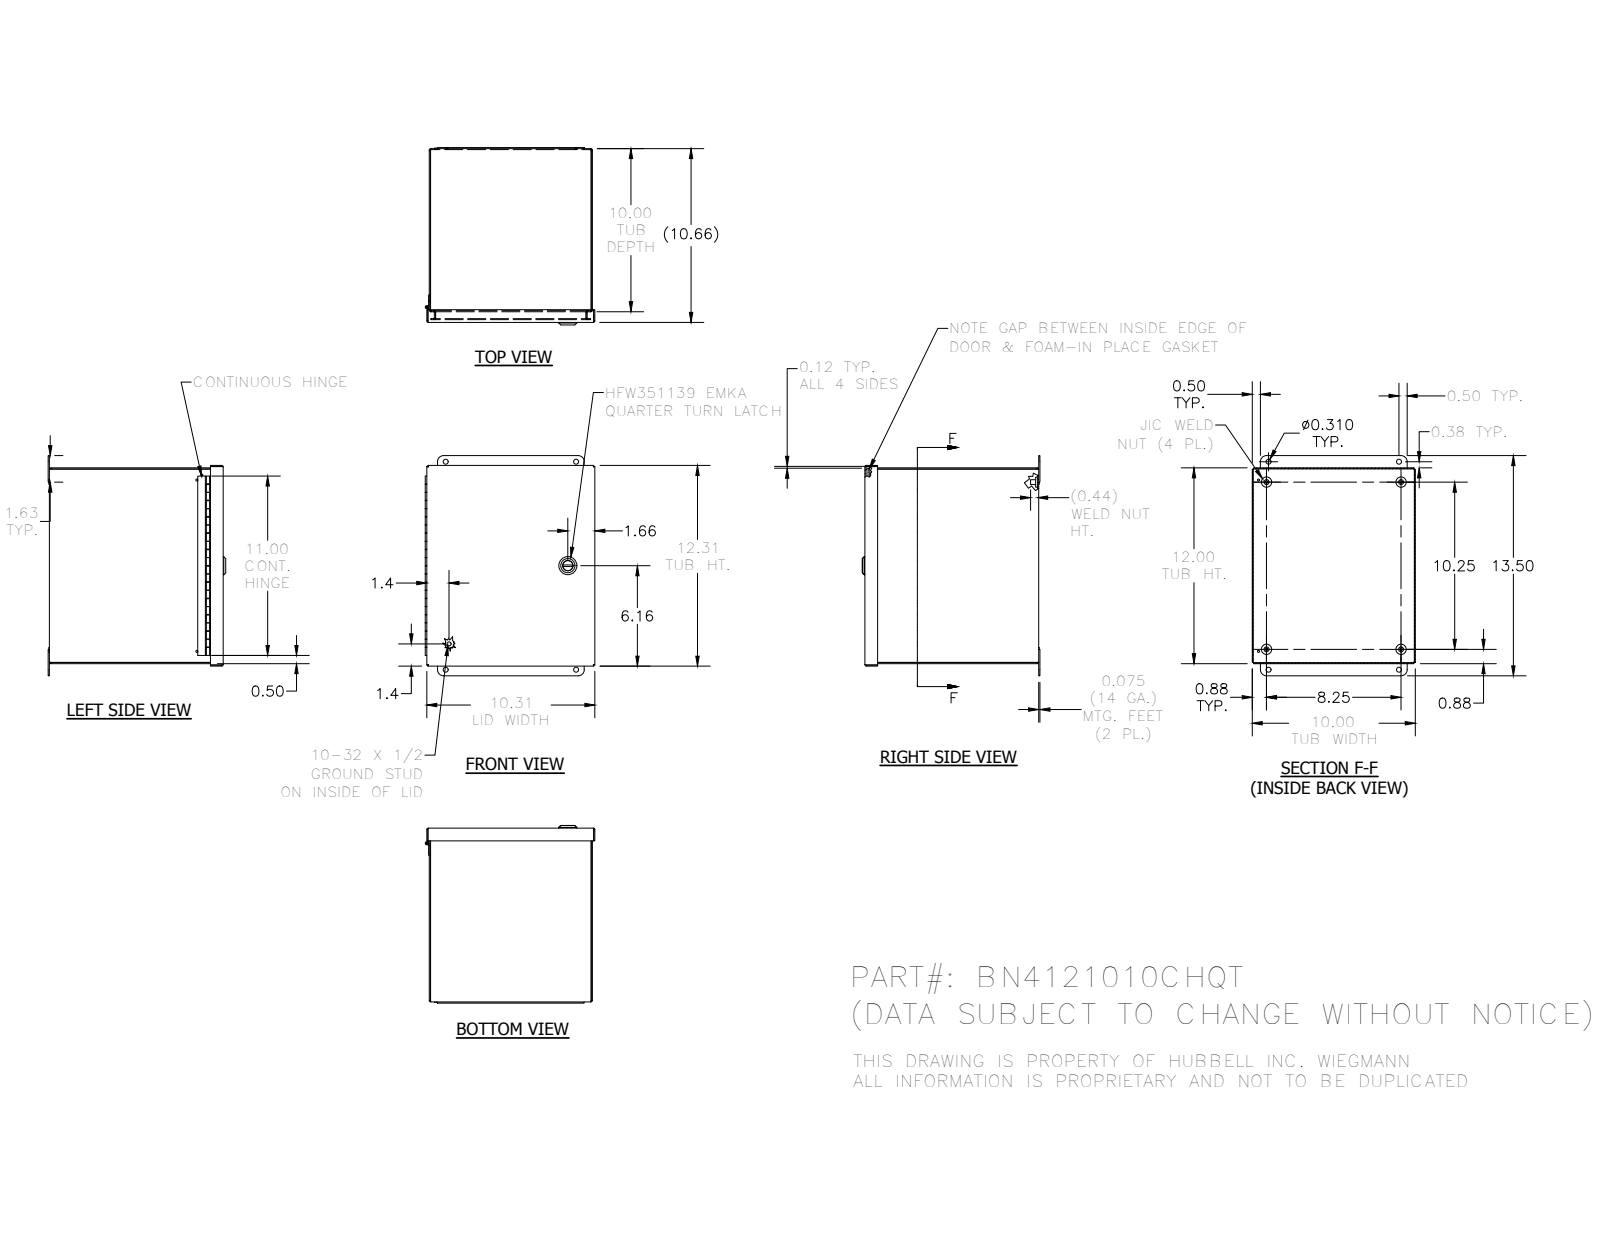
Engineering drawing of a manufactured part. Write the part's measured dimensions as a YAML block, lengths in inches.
part_name: "BN4121010CHQT"
step_written_by: "SolidWorks 2018 (AUTOMOTIVE_DESIGN)"
units: inches
bodies: {solids: 21, faces: 809, planar: 408, cylindrical: 273, other: 128}
overall_size: [13.5, 10.888, 10.406]
volume: 54.38
surface_area: 1682
round_holes:
  - {diameter: 0.12, count: 9}
  - {diameter: 0.156, count: 4}
  - {diameter: 0.31, count: 4}
  - {diameter: 0.116, count: 1}
  - {diameter: 0.197, count: 1}
  - {diameter: 0.315, count: 1}
  - {diameter: 0.394, count: 1}
  - {diameter: 0.402, count: 1}
  - {diameter: 0.634, count: 1}
  - {diameter: 0.802, count: 1}
round_bosses_or_shafts:
  - {diameter: 0.625, count: 4}
  - {diameter: 0.3, count: 4}
  - {diameter: 1.102, count: 1}
  - {diameter: 0.866, count: 1}
  - {diameter: 0.78, count: 1}
  - {diameter: 0.622, count: 1}
  - {diameter: 0.598, count: 1}
  - {diameter: 0.531, count: 1}
partial_cylinders:
  - {radius: 0.012, count: 30}
  - {radius: 0.031, count: 20}
  - {radius: 0.093, count: 20}
  - {radius: 0.125, count: 16}
  - {radius: 0.02, count: 12}
  - {radius: 0.157, count: 4}
  - {radius: 0.375, count: 4}
  - {radius: 0.016, count: 2}
face_to_face_distances: [0.062, 0.062, 11.938, 10.594, 9.876, 9.938, 10, 9.938, 10.656, 10.532]
hole_center_spacings: [14.081, 0.737, 1.256, 5.09, 7.907, 8, 8.015, 8.032]
